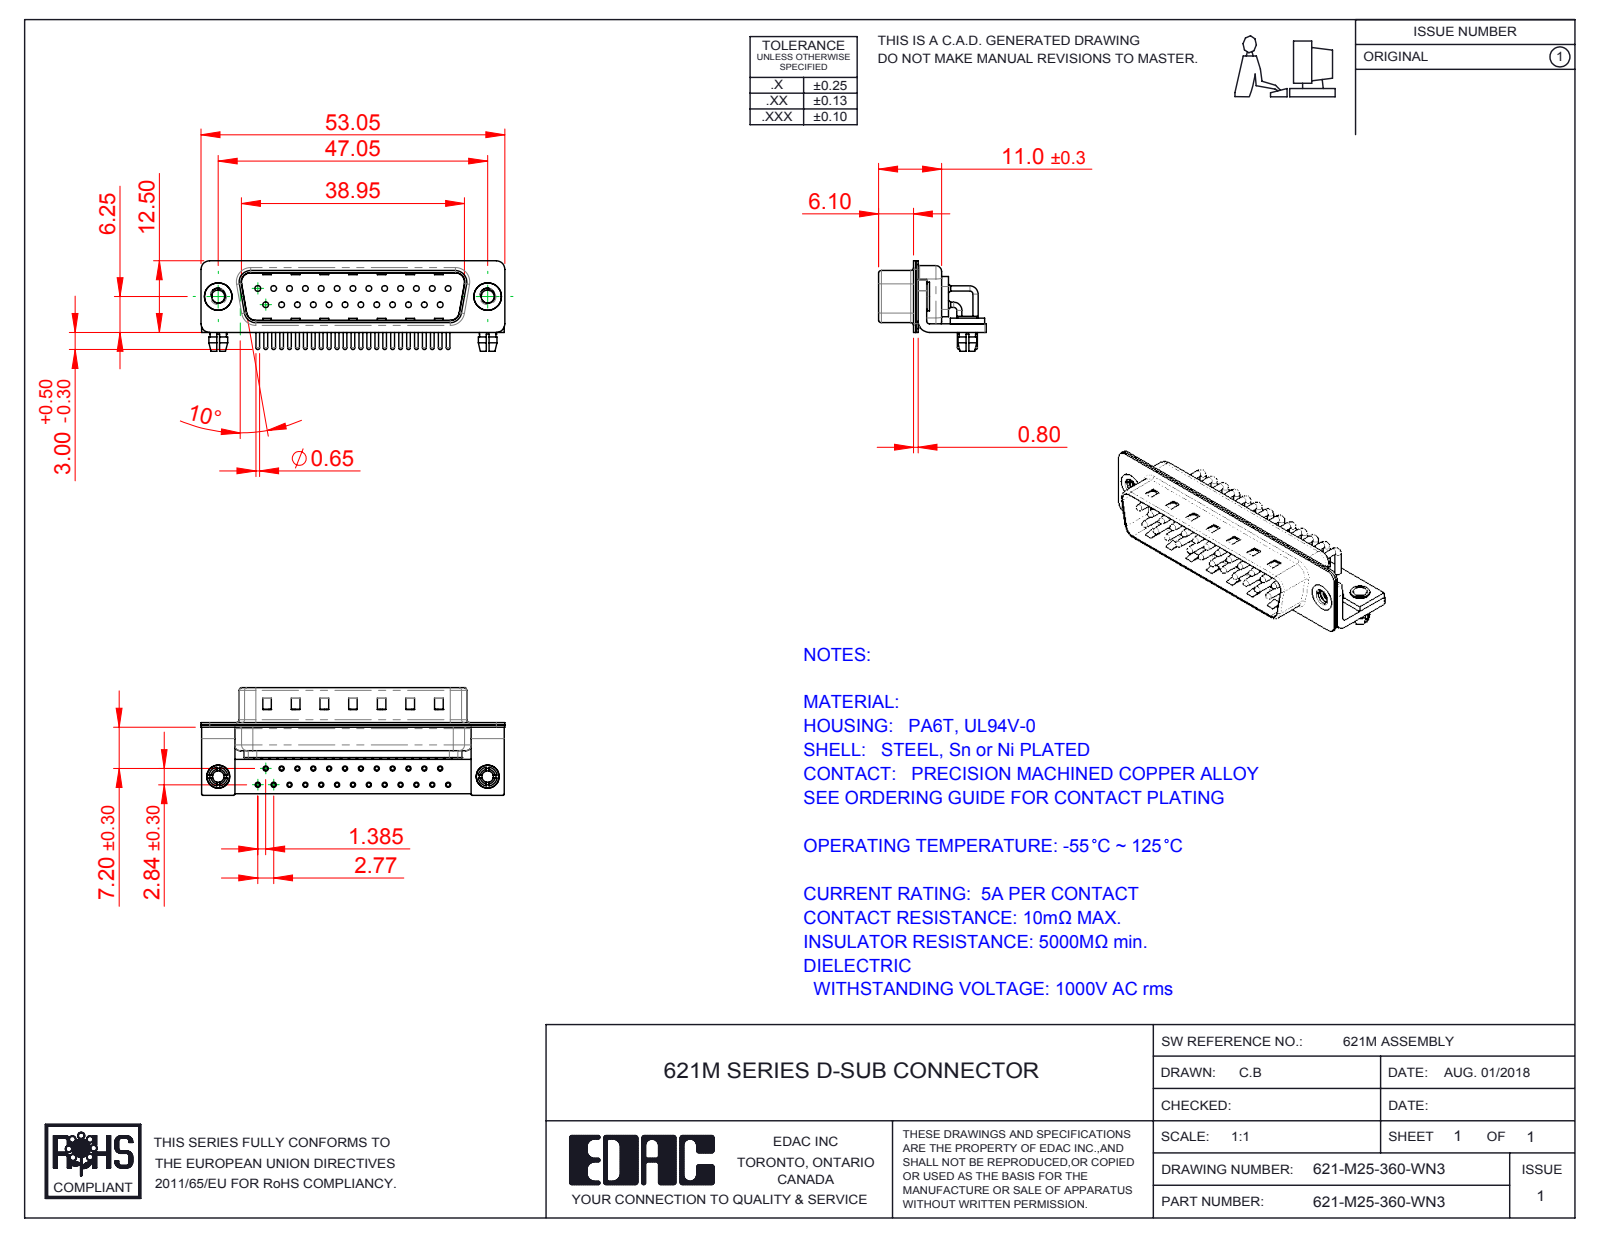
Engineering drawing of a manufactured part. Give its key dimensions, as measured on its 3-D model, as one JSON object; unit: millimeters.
{"part_name": "621M Stabilizer Bracket; 621-M25-360-WN3; 621M Board Lock; 621M Housing_25 Contacts (+6 more)", "step_written_by": "SolidWorks 2016 (CONFIG_CONTROL_DESIGN)", "units": "millimeters", "bodies": {"solids": 35, "faces": 3318, "planar": 1845, "cylindrical": 1141, "other": 332}, "overall_size": [53.05, 18.8, 15.8], "volume_mm3": 3431, "surface_area_mm2": 9130, "round_holes": [[2, 27], [0.9, 25], [1, 25], [1.7, 25], [2.26, 2], [2.5, 2], [3.2, 2], [4, 2], [4.8, 2]], "round_bosses_or_shafts": [[0.9, 33], [1.5, 25], [0.65, 25], [5, 2], [4.9, 2], [4, 2], [3.4, 2], [3.3, 2]], "partial_cylinders_radius": [[1.01, 25], [0.25, 16], [1.5, 16], [2, 13], [0.5, 9], [1.6, 8], [0.6, 4], [0.65, 4]], "face_to_face_distances": [0.4, 0.85, 1.25, 1.5, 9.55, 10.4, 0.8, 1, 8.3, 8.7], "hole_center_spacings": [3.16, 2.77, 8.31, 5.54, 11.08, 13.85, 5.04, 16.62]}
